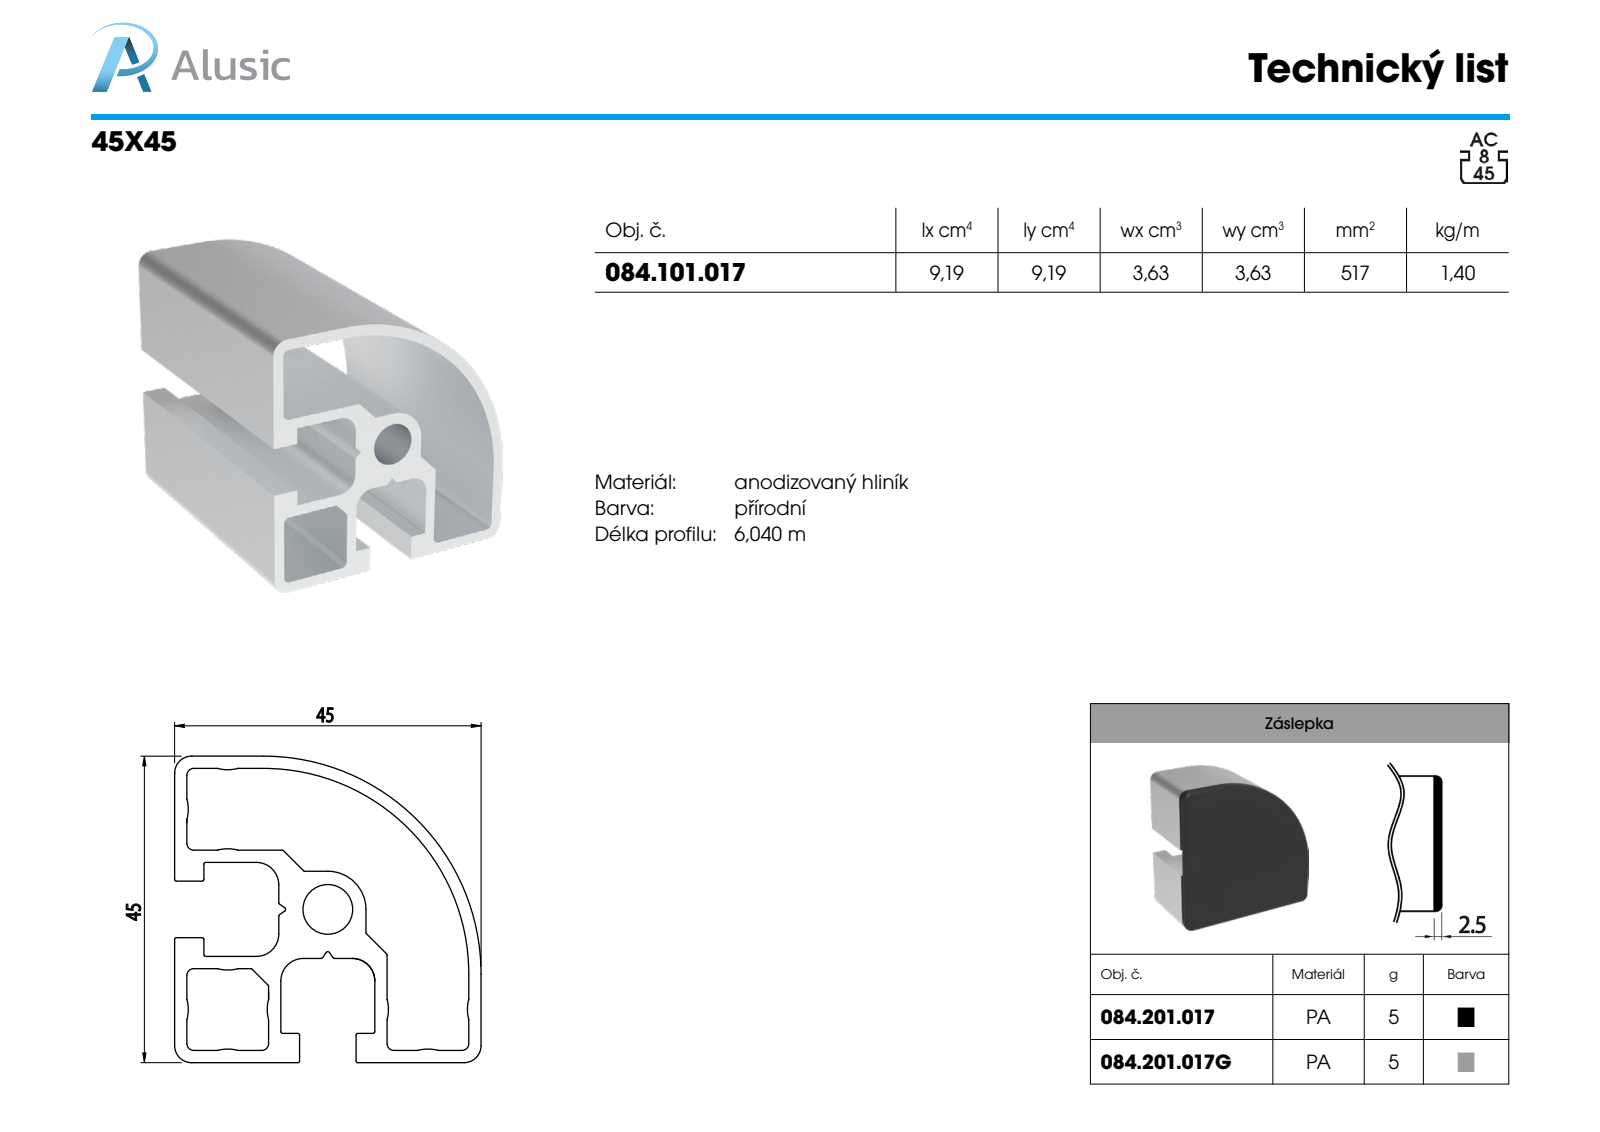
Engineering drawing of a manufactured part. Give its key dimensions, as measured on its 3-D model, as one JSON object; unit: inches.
{"part_name": "084.101.017", "step_written_by": "SolidWorks 2018 (AUTOMOTIVE_DESIGN)", "units": "inches", "bodies": {"solids": 1, "faces": 62, "planar": 43, "cylindrical": 19, "other": 0}, "overall_size": [3.937, 1.772, 1.772], "volume_in3": 3.134, "surface_area_in2": 72.28, "round_holes": [[0.287, 1]], "partial_cylinders_radius": [[0.039, 7], [0.118, 4], [0.098, 3], [0.22, 1], [1.189, 1], [1.26, 1]], "face_to_face_distances": [0.071, 0.543, 1.157, 0.614, 1.228, 1.701, 0.472, 1.087, 1.772, 1.63]}
